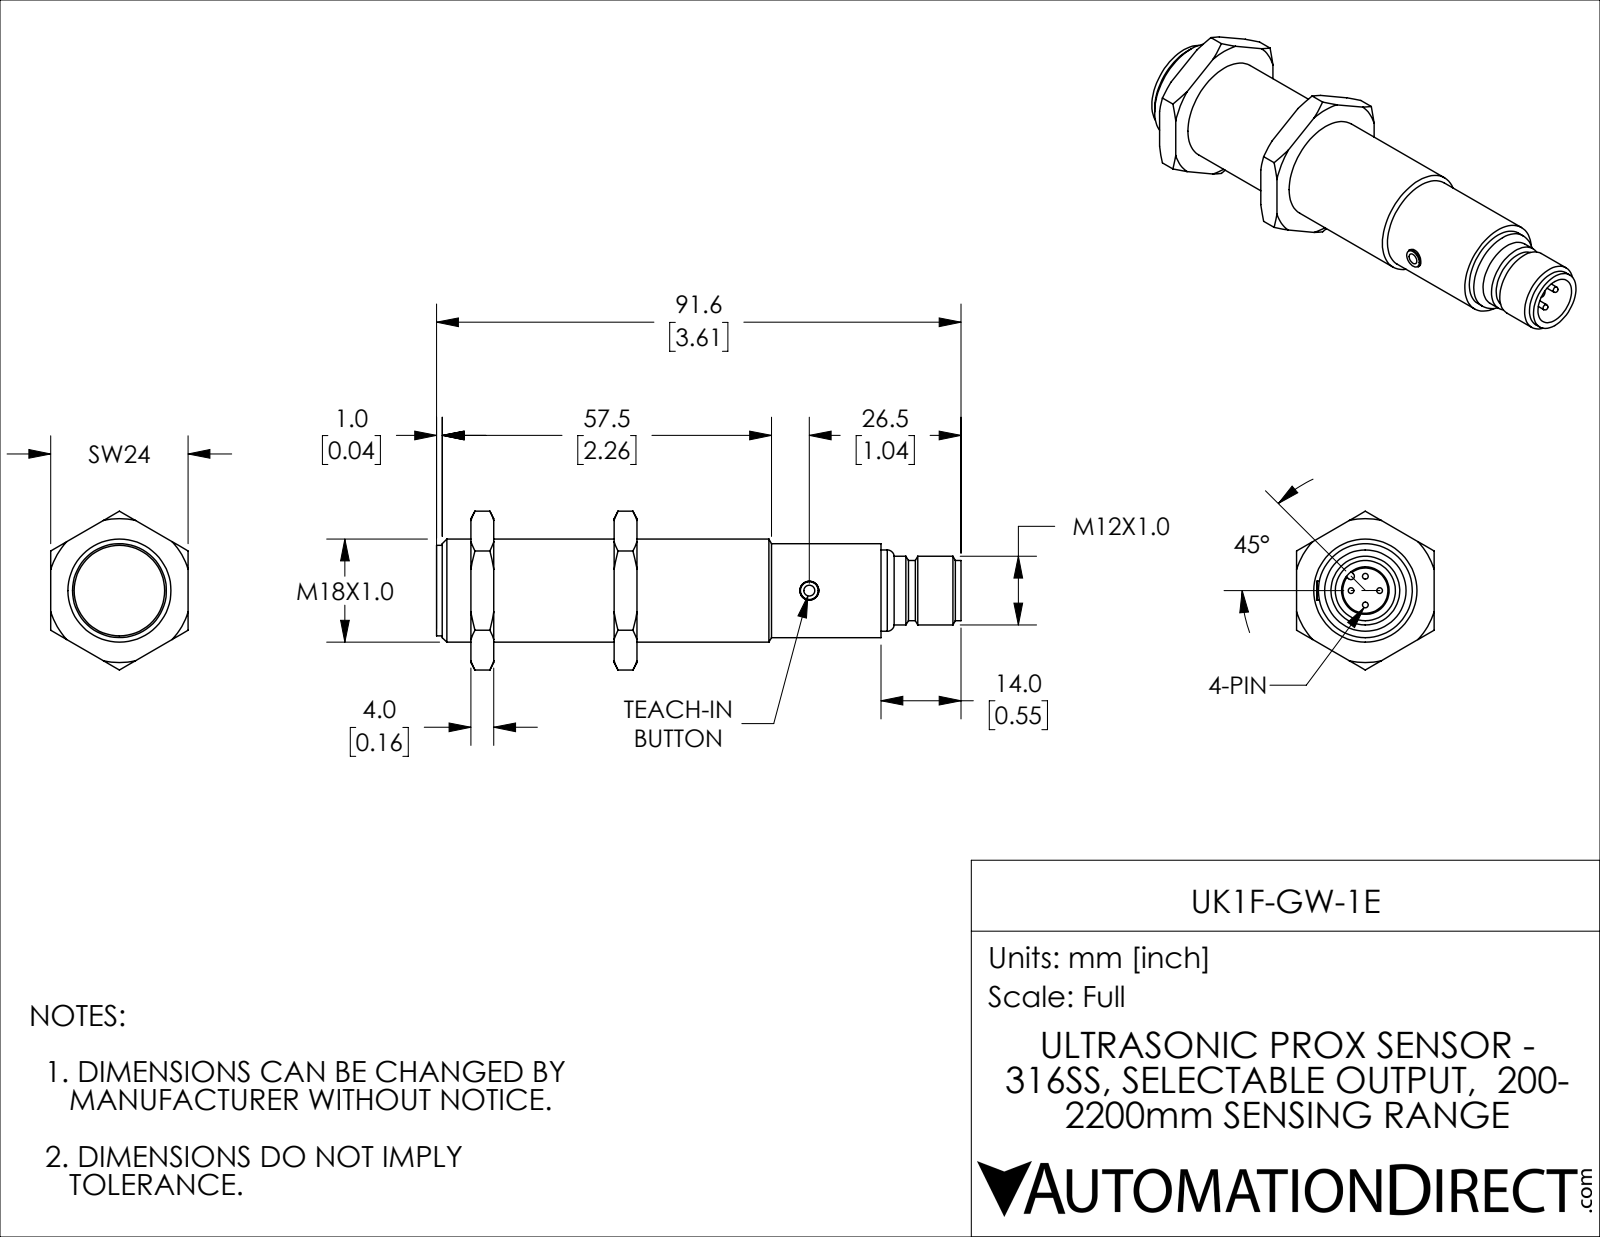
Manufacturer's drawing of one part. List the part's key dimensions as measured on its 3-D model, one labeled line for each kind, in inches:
Part name (STEP PRODUCT): UK1F-GW-1E
STEP written by: SolidWorks 2018 (AUTOMOTIVE_DESIGN)
Units: inches
Bodies: 4 solids, 113 faces (27 planar, 35 cylindrical, 51 other)
Overall size (bounding box): 3.606 × 1.091 × 0.945
Volume: 1.338 in³ · Surface area: 11.97 in²
Round holes (diameter × count): ⌀0.13 ×1, ⌀0.327 ×1, ⌀0.709 ×1
Round bosses / shafts (diameter × count): ⌀0.039 ×4, ⌀0.646 ×1, ⌀0.622 ×1, ⌀0.559 ×1, ⌀0.472 ×1, ⌀0.413 ×1
Partial cylindrical surfaces — rounded edges, fillets, slot ends (radius × count): R0.024 ×1
Main face-to-face distances: 0.984, 0.157, 0.945, 1.142, 0.827, 0.236, 0.394, 1.22, 1.378, 3.055
